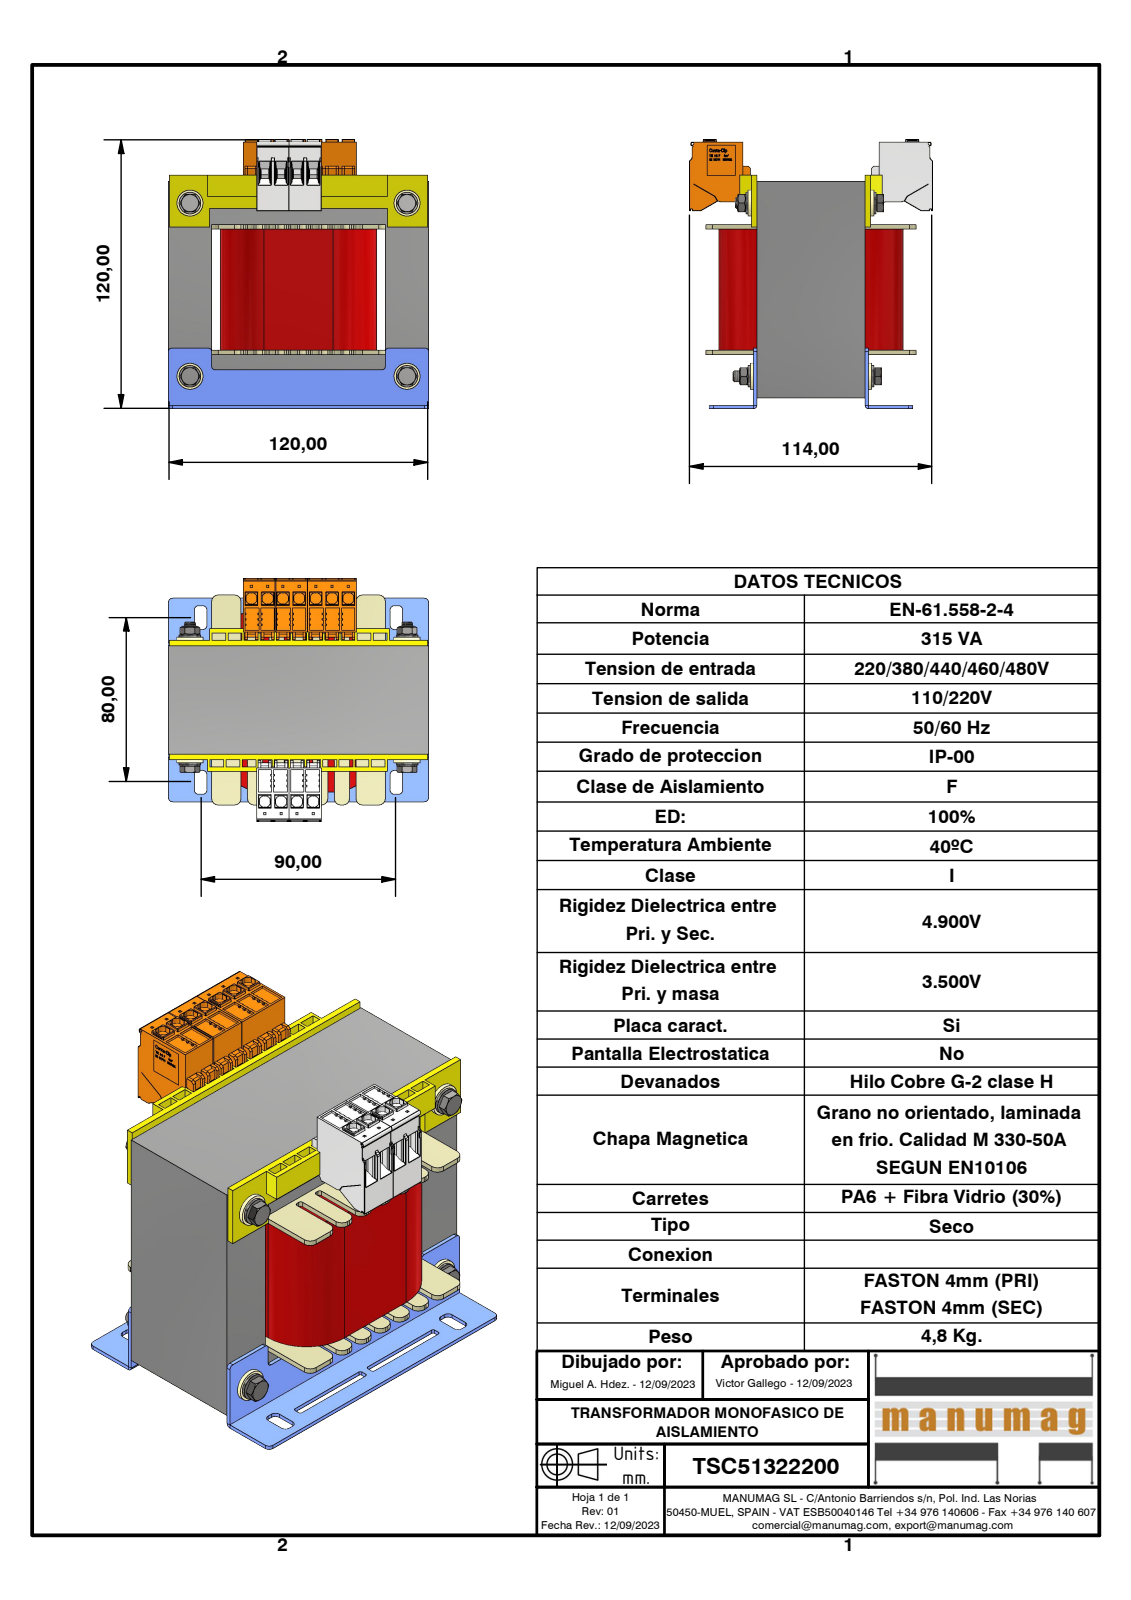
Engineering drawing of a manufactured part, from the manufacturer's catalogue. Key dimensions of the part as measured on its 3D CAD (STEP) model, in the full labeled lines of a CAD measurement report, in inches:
Part name (STEP PRODUCT): TSC51322200; EI120 x 100 - 50 (Rc40); AF40DIN; EI 120 X 100 - 50 (+8 more)
STEP written by: Autodesk Inventor 2023 (AUTOMOTIVE_DESIGN)
Units: inches
Bodies: 35 solids, 9262 faces (7528 planar, 1175 cylindrical, 559 other)
Overall size (bounding box): 4.902 × 4.724 × 4.421
Volume: 47.96 in³ · Surface area: 286.7 in²
Round holes (diameter × count): ⌀0.163 ×4, ⌀0.197 ×4, ⌀0.209 ×4, ⌀0.26 ×4, ⌀0.268 ×2
Round bosses / shafts (diameter × count): ⌀0.472 ×4, ⌀0.394 ×4, ⌀0.264 ×4, ⌀0.232 ×4, ⌀0.18 ×4
Partial cylindrical surfaces — rounded edges, fillets, slot ends (radius × count): R0.006 ×431, R0.008 ×122, R0.039 ×32, R0.02 ×30, R0.118 ×28, R0.079 ×20, R0.031 ×18, R0.012 ×12
Main face-to-face distances: 3.15, 0.787, 1.575, 1.969, 2.362, 3.937, 0.059, 0.63, 2.205, 3.346
Hole centre spacings: 3.15, 3.937, 5.042
